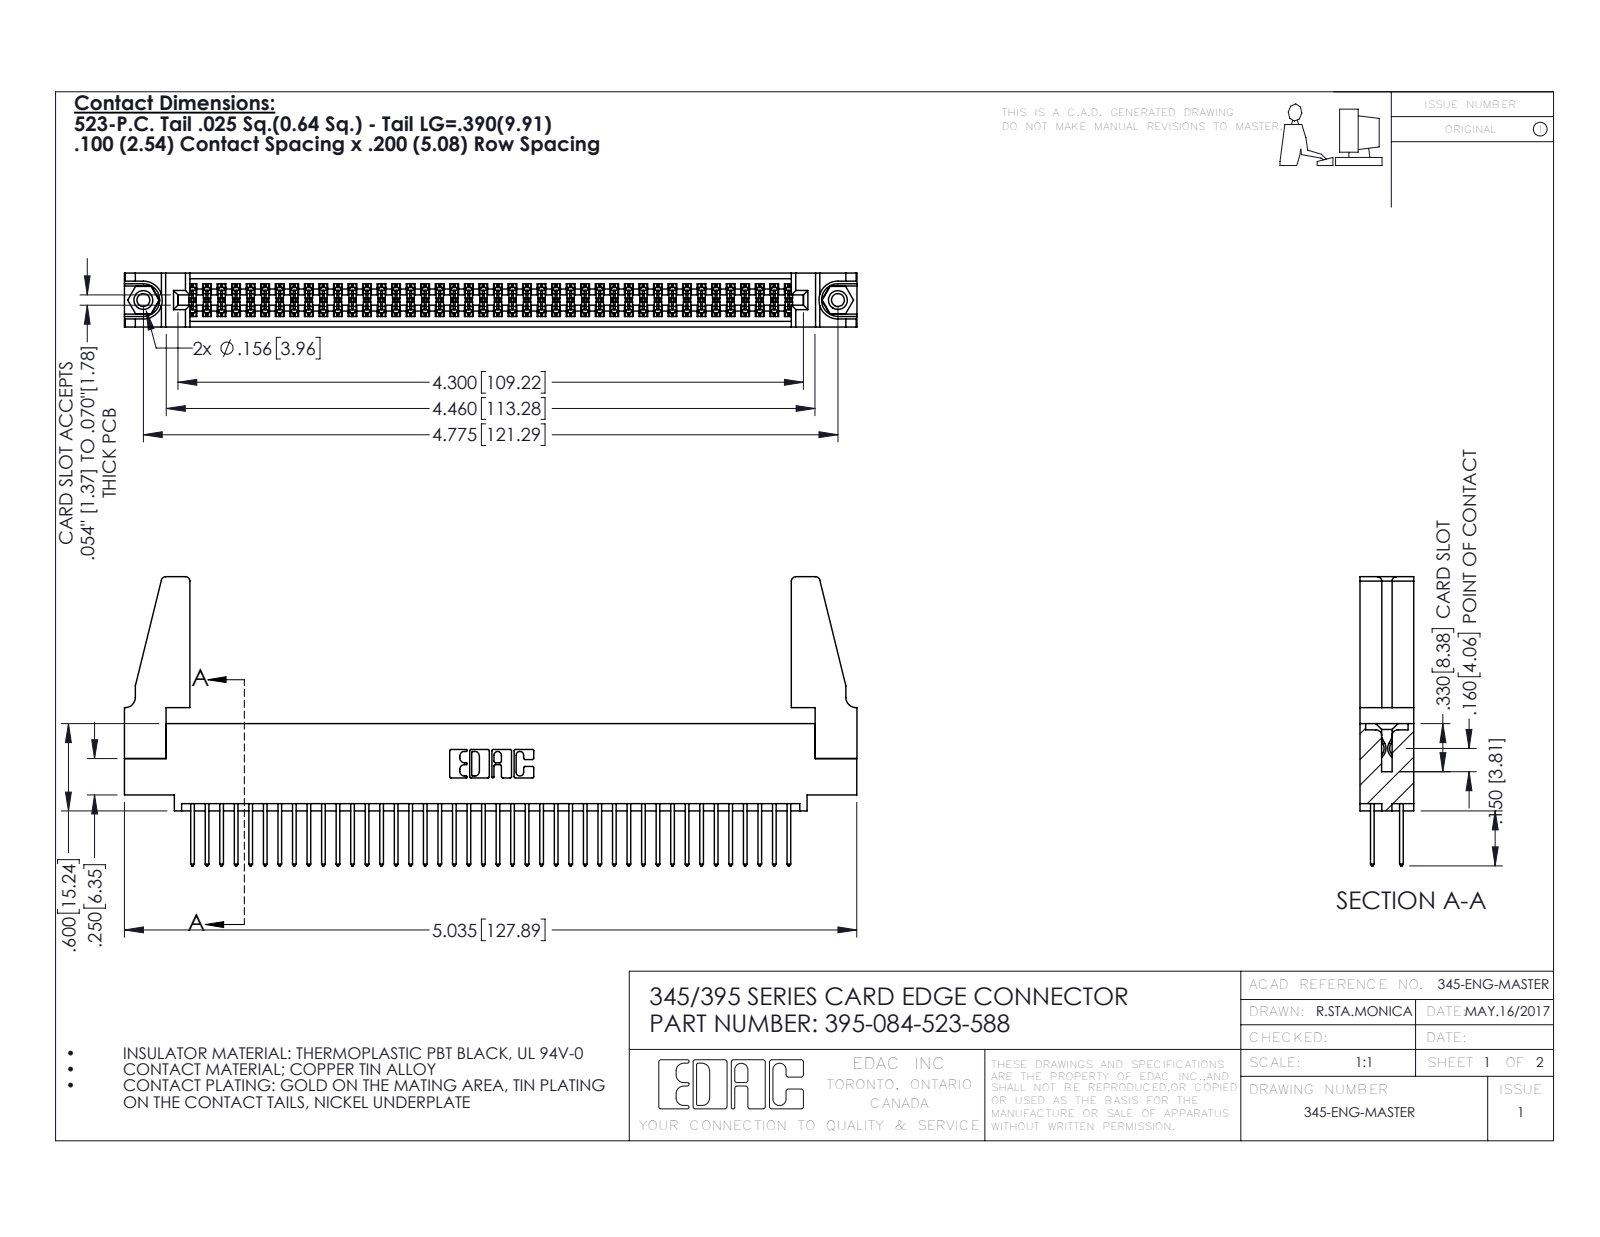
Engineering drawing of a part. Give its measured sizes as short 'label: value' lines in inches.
name: 345-250-001_345-250-001-102; 345 Part_0.110 Offset - 0.156 Dia-TH; 345-292-001_345-293-123; 395-084-523-588 (+1 more)
written by: SolidWorks 2016 (CONFIG_CONTROL_DESIGN)
unit: in
bodies: 89 solids, 4454 faces (2928 planar, 1510 cylindrical, 16 other)
size: 5.036 × 1.987 × 0.37
volume: 0.963 in³; area: 34.88 in²
holes: 2× ⌀0.089, 2× ⌀0.125, 2× ⌀0.156, 1× ⌀0.064
bosses: 2× ⌀0.155
rounds: 126× R0.006, 84× R0.01, 22× R0.01, 8× R0.03, 6× R0.007, 6× R0.031, 3× R0.026, 2× R0.014
face distances: 0.072, 0.298, 0.37, 0.2, 0.098, 0.272, 0.025, 0.225, 0.175, 0.149
hole spacings: 0.27, 4.539, 4.775
